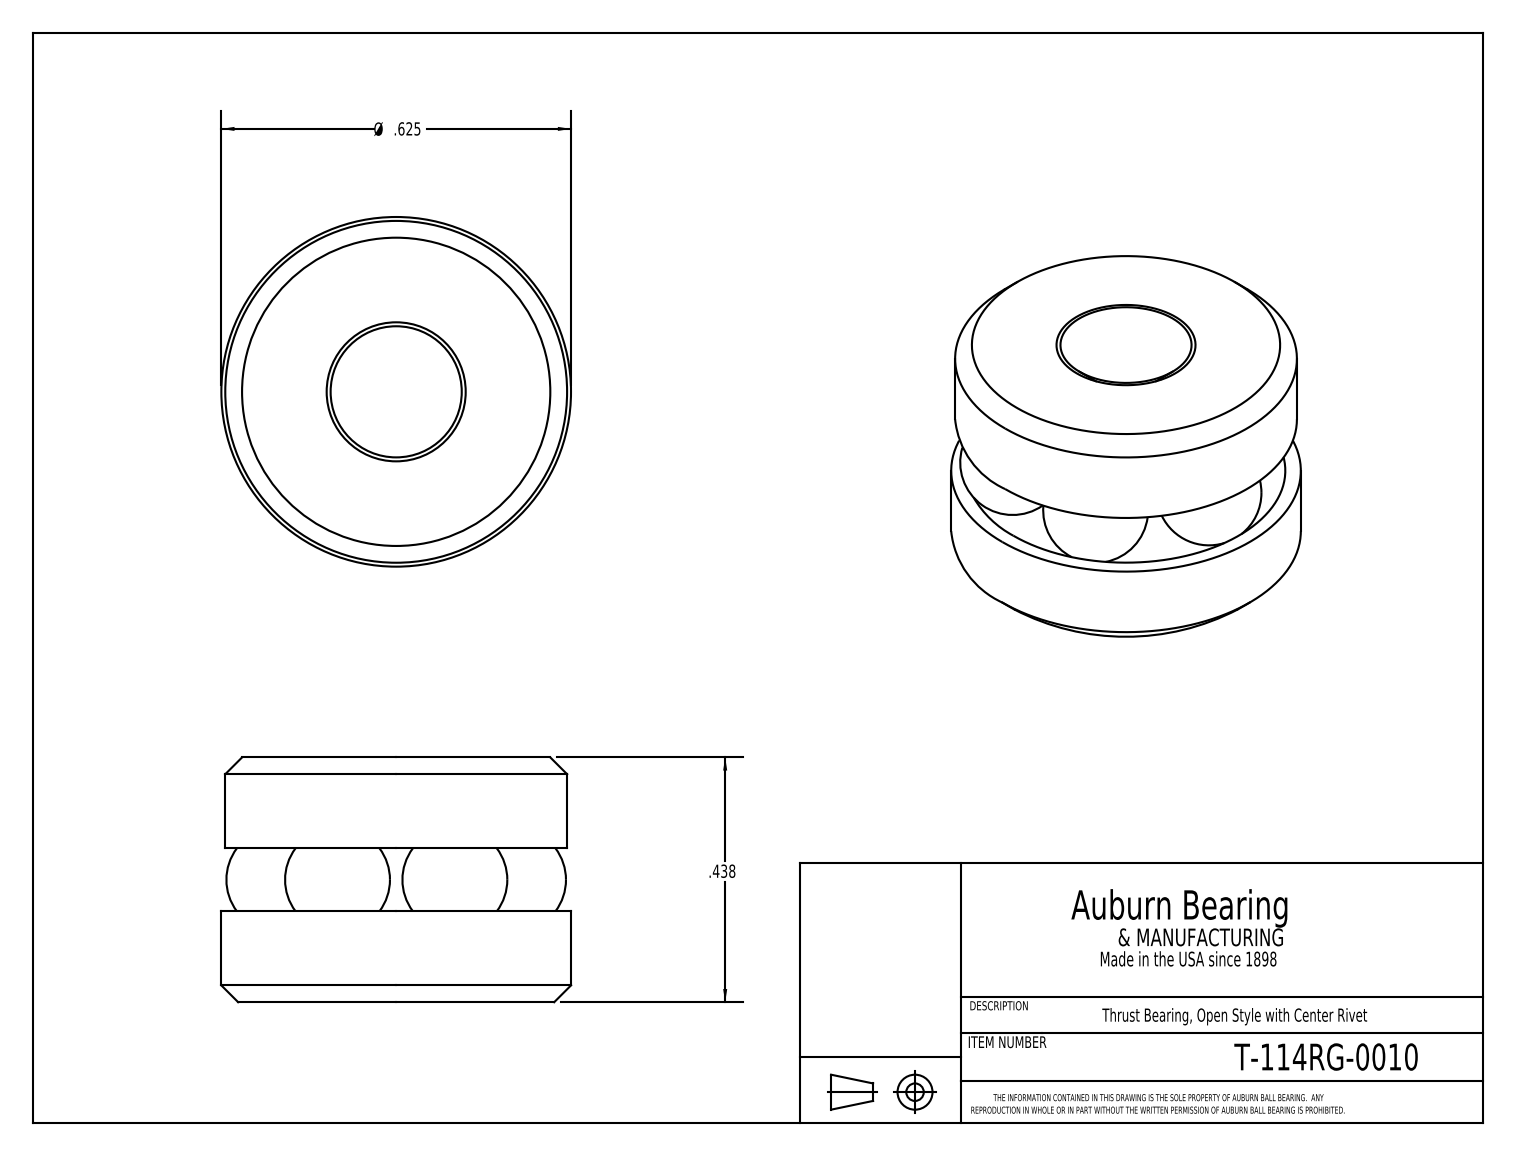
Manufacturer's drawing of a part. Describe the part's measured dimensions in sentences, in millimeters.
The part is named "T-114RG_T-114RG-0010". Its 3-D file was written by "SolidWorks 2016 (CONFIG_CONTROL_DESIGN)". It is 9 solids with 27 faces: 8 planar, 5 cylindrical and 14 other. Overall it measures 15.9 by 15.9 by 11.1 millimeters. Its volume is 1 750 cubic millimeters and its surface area 1 838 square millimeters. Round holes: 1 of diameter 3.4. Round bosses or shafts: 1 of diameter 15.9, 1 of diameter 15.5, 1 of diameter 3.2. The main face-to-face distances are 11.1, 4.1, 7, 7, 2.9, 4.1.
